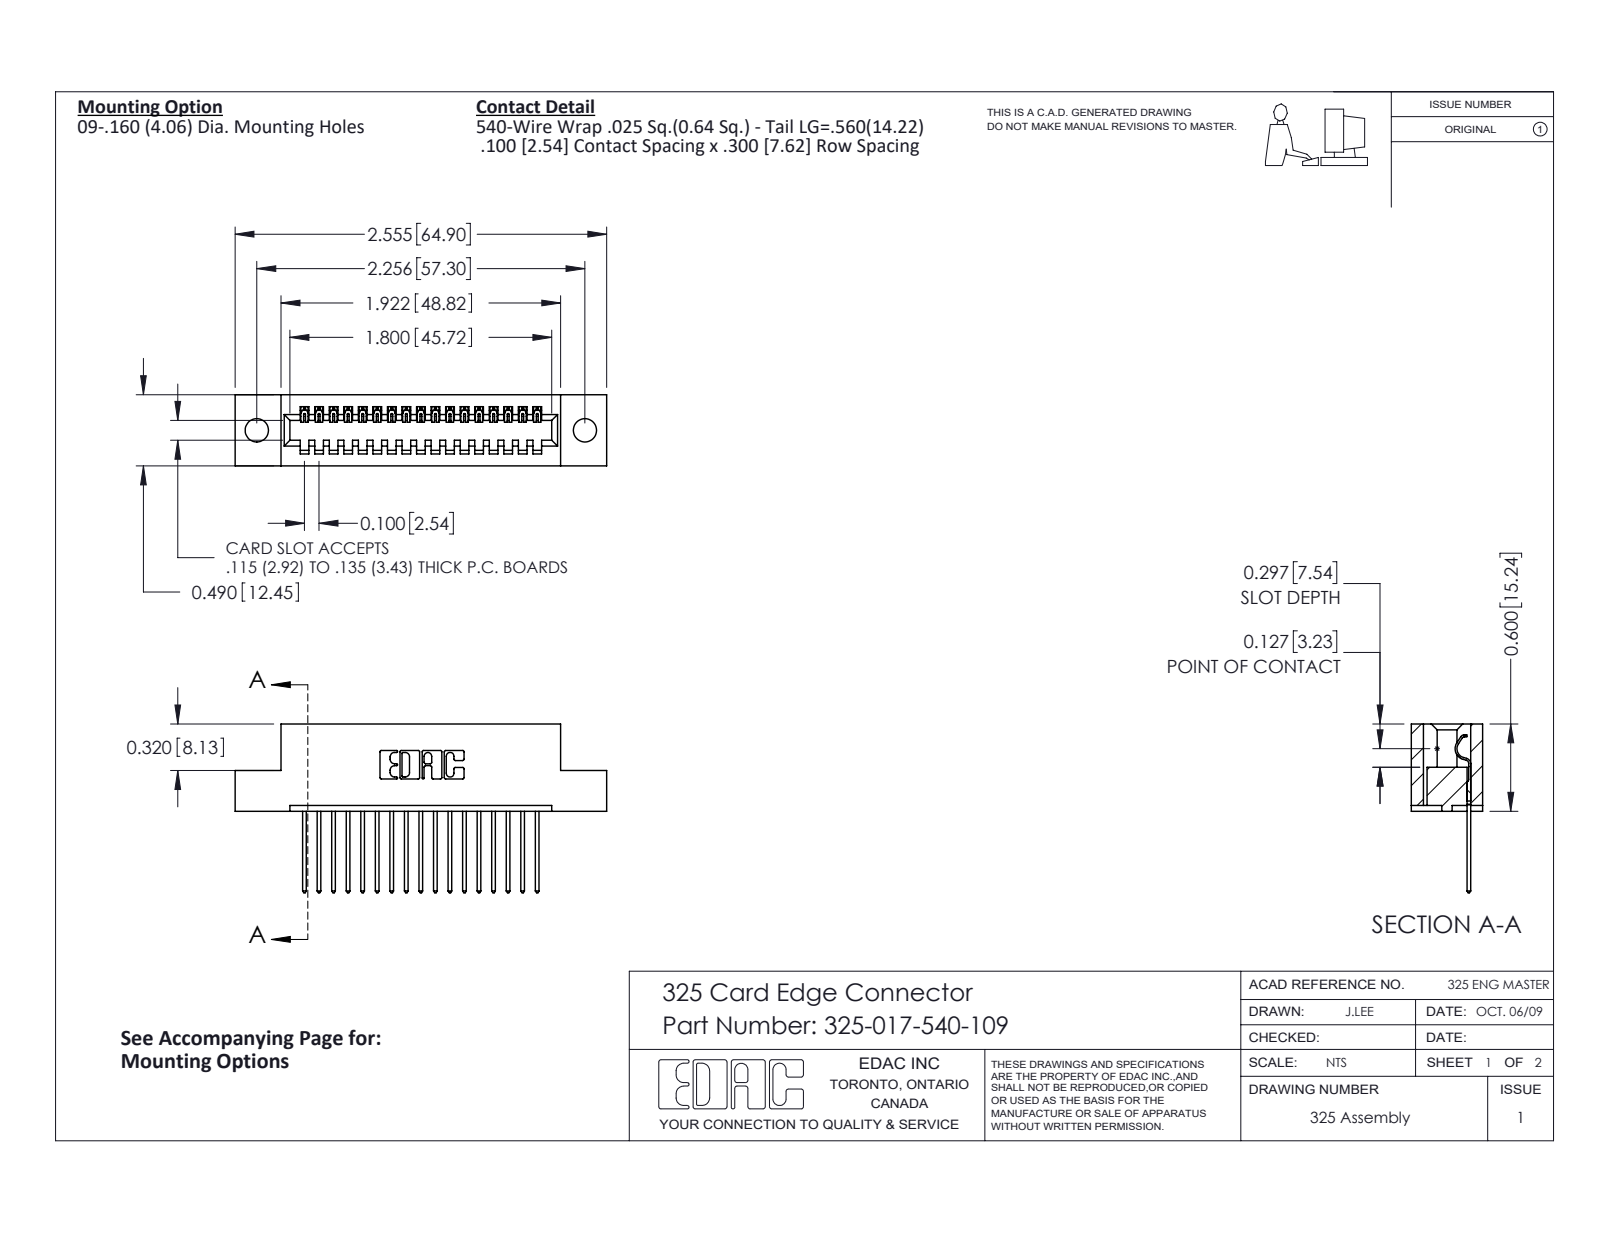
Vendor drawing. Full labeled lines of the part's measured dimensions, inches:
Part name (STEP PRODUCT): 325-292-001_325-293-140; 325 Part_.160 TH; 325-017-540-109
STEP written by: SolidWorks 2016 (CONFIG_CONTROL_DESIGN)
Units: inches
Bodies: 18 solids, 1100 faces (784 planar, 316 cylindrical, 0 other)
Overall size (bounding box): 2.555 × 1.16 × 0.49
Volume: 0.478 in³ · Surface area: 12.71 in²
Round holes (diameter × count): ⌀0.16 ×2
Partial cylindrical surfaces — rounded edges, fillets, slot ends (radius × count): R0.006 ×34, R0.01 ×34, R0.01 ×22, R0.007 ×6, R0.031 ×6, R0.026 ×3, R0.014 ×1, R0.022 ×1
Main face-to-face distances: 0.083, 0.407, 0.3, 0.49, 0.107, 0.383, 0.025, 0.6, 0.04, 0.56
Hole centre spacings: 2.256
